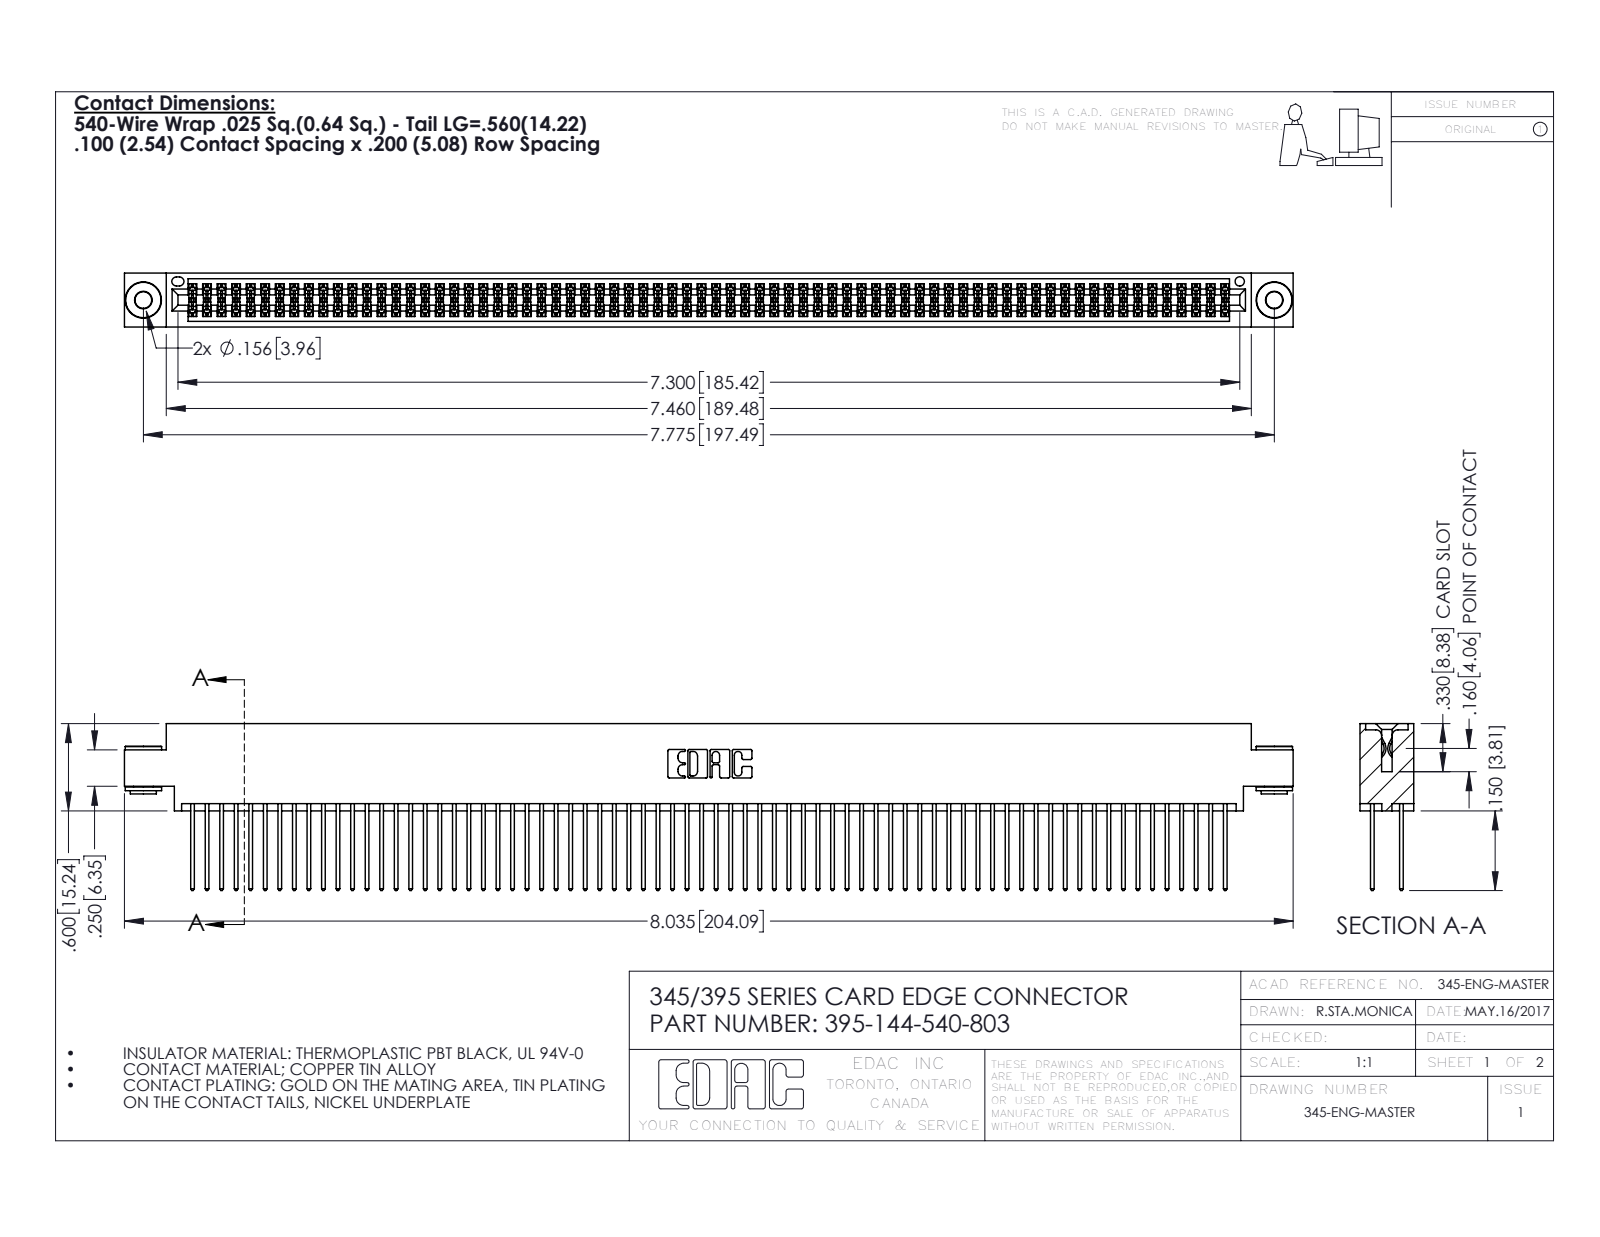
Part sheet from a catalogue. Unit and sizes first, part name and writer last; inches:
Units: inches
Overall size (bounding box): 8.035 × 1.147 × 0.37
Round holes (diameter × count): ⌀0.116 ×2, ⌀0.156 ×2, ⌀0.064 ×1
Round bosses / shafts (diameter × count): ⌀0.25 ×2, ⌀0.18 ×2, ⌀0.136 ×2
Partial cylindrical surfaces — rounded edges, fillets, slot ends (radius × count): R0.006 ×216, R0.01 ×144, R0.01 ×22, R0.007 ×6, R0.031 ×6, R0.026 ×3, R0.014 ×2, R0.019 ×2
Main face-to-face distances: 0.072, 0.298, 0.2, 0.098, 0.272, 0.025, 0.37, 0.225, 0.175, 0.149
Hole centre spacings: 0.27, 7.539, 7.775
Volume: 1.254 in³ · Surface area: 52.46 in²
Bodies: 147 solids, 7368 faces (4846 planar, 2514 cylindrical, 8 other)
Part name (STEP PRODUCT): 345-292-001_345-293-140; 395-144-540-803; 345-250-002_345-250-002-102; 345 Part_0.170 Offset - 0.156 Dia-TH
STEP written by: SolidWorks 2016 (CONFIG_CONTROL_DESIGN)
